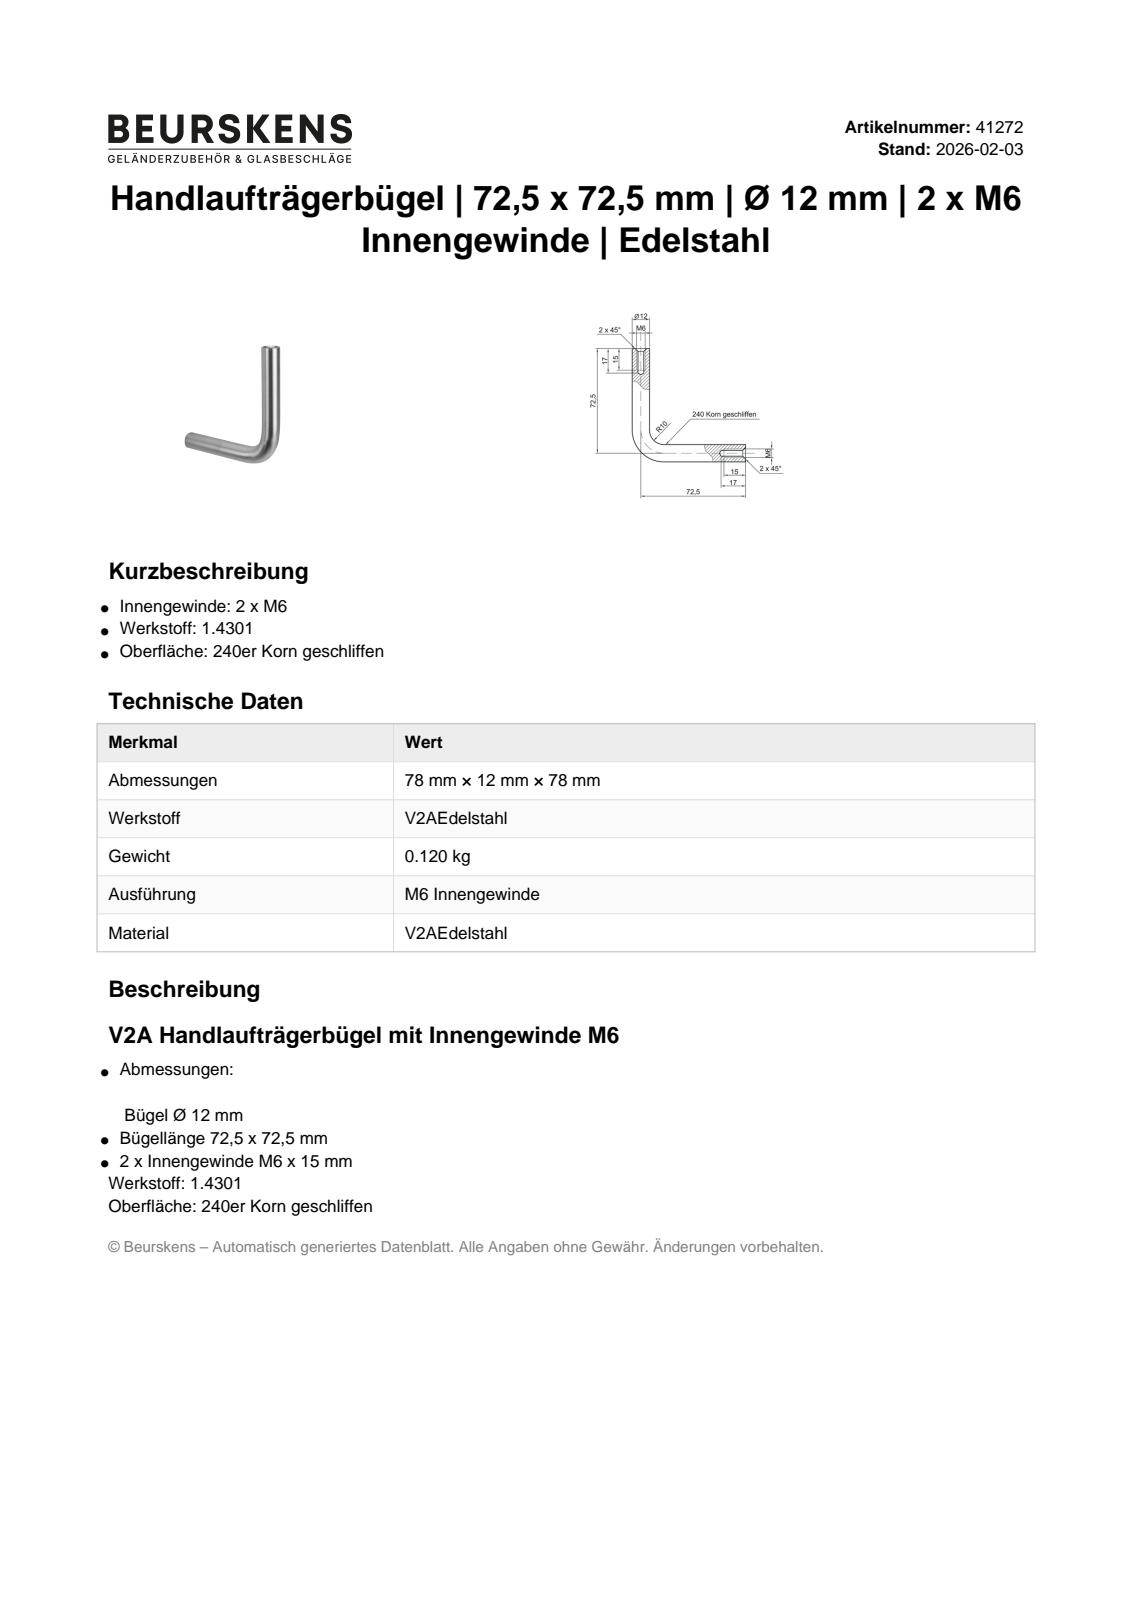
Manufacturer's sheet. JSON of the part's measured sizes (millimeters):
{"part_name": "41272", "step_written_by": "Autodesk Inventor 2022 (AUTOMOTIVE_DESIGN)", "units": "millimeters", "bodies": {"solids": 1, "faces": 9, "planar": 4, "cylindrical": 2, "other": 3}, "overall_size": [78.5, 78.5, 12], "volume_mm3": 14742, "surface_area_mm2": 6130, "round_holes": [[6, 2]], "face_to_face_distances": [17]}
